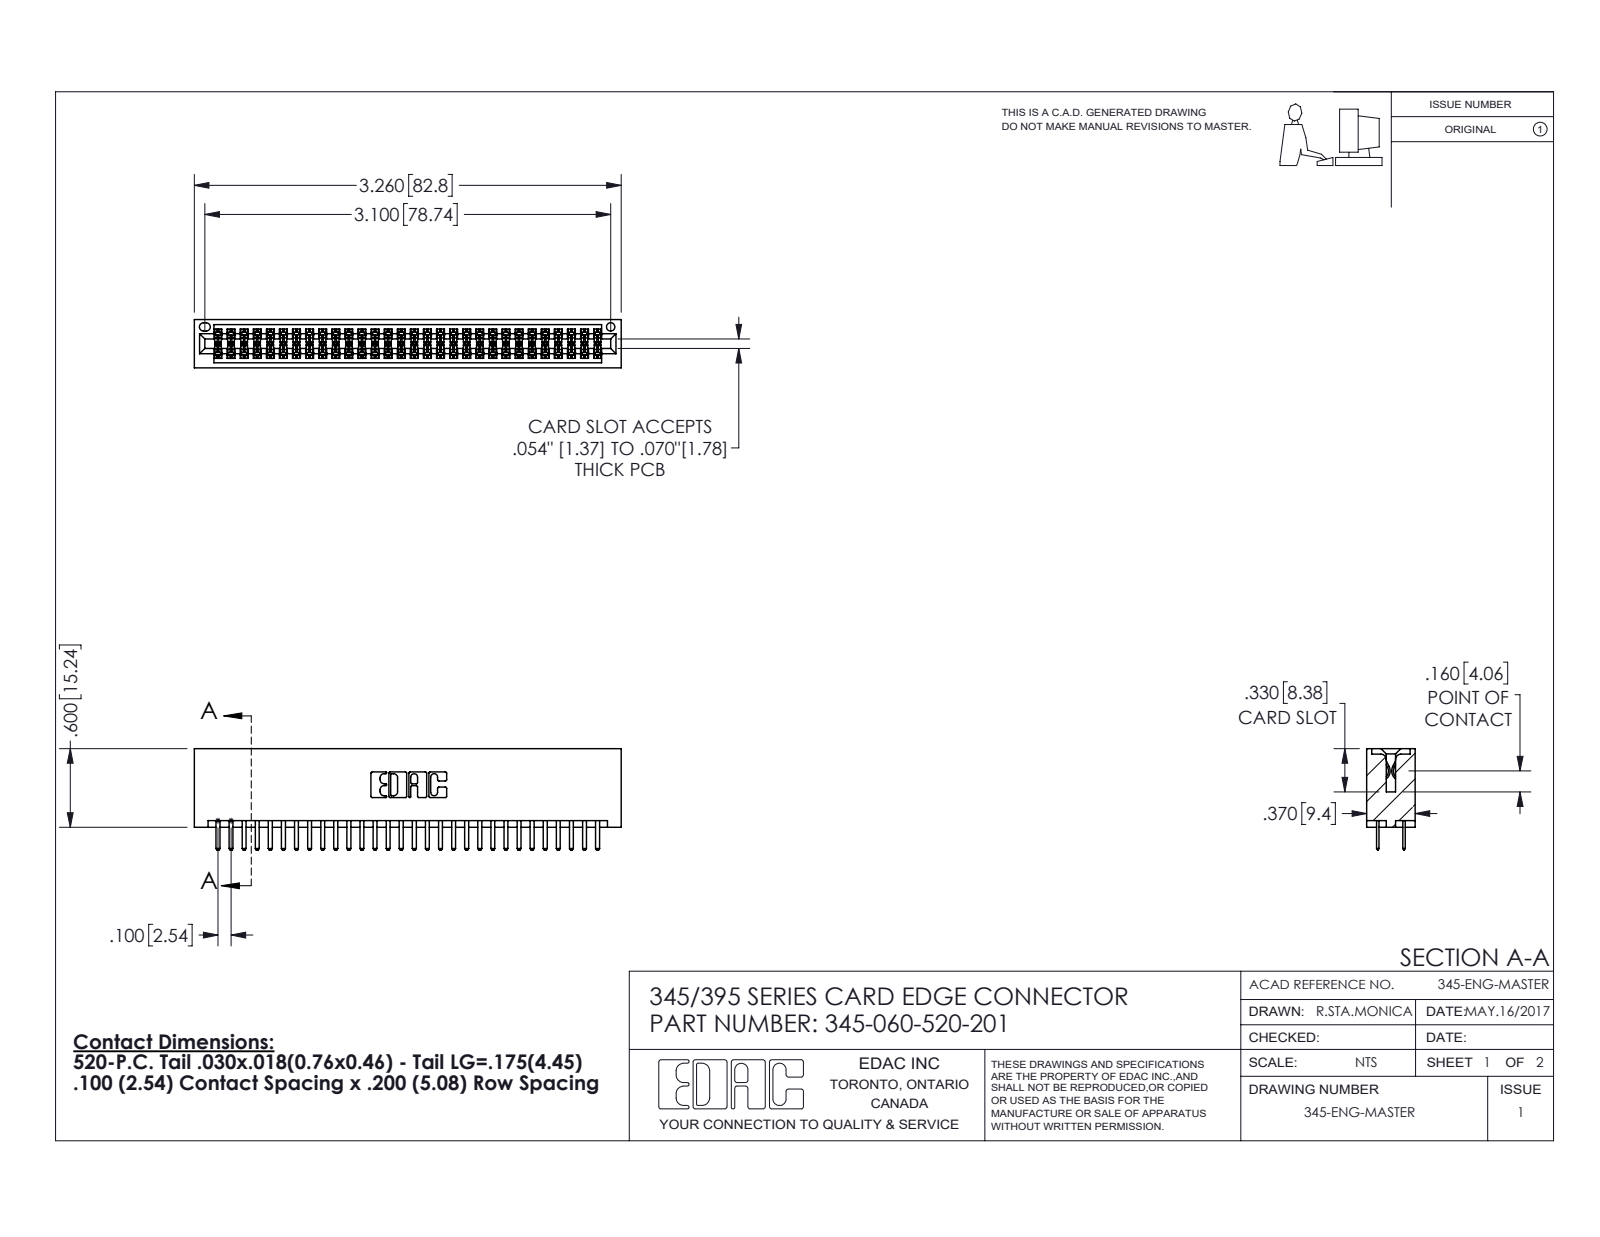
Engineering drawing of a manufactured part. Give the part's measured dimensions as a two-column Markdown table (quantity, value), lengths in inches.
| quantity | value |
| --- | --- |
| part name | 345-060-520-201; 345-292-001_345-293-120; 345 Part_No Mounting Lugs |
| STEP written by | SolidWorks 2016 (CONFIG_CONTROL_DESIGN) |
| units | inches |
| bodies | 61 solids, 3358 faces (2176 planar, 1182 cylindrical, 0 other) |
| overall size | 3.26 × 0.775 × 0.37 |
| volume | 0.52 in³ |
| surface area | 19.55 in² |
| round holes (diameter × count) | 0.064 × 1 |
| partial cylindrical surfaces (radius × count) | 0.006 × 90, 0.01 × 64, 0.01 × 22, 0.007 × 6, 0.031 × 6, 0.026 × 3, 0.014 × 2, 0.019 × 2 |
| main face-to-face distances | 0.298, 0.072, 0.2, 0.37, 0.098, 0.272, 0.025, 0.225, 0.022, 0.072 |
